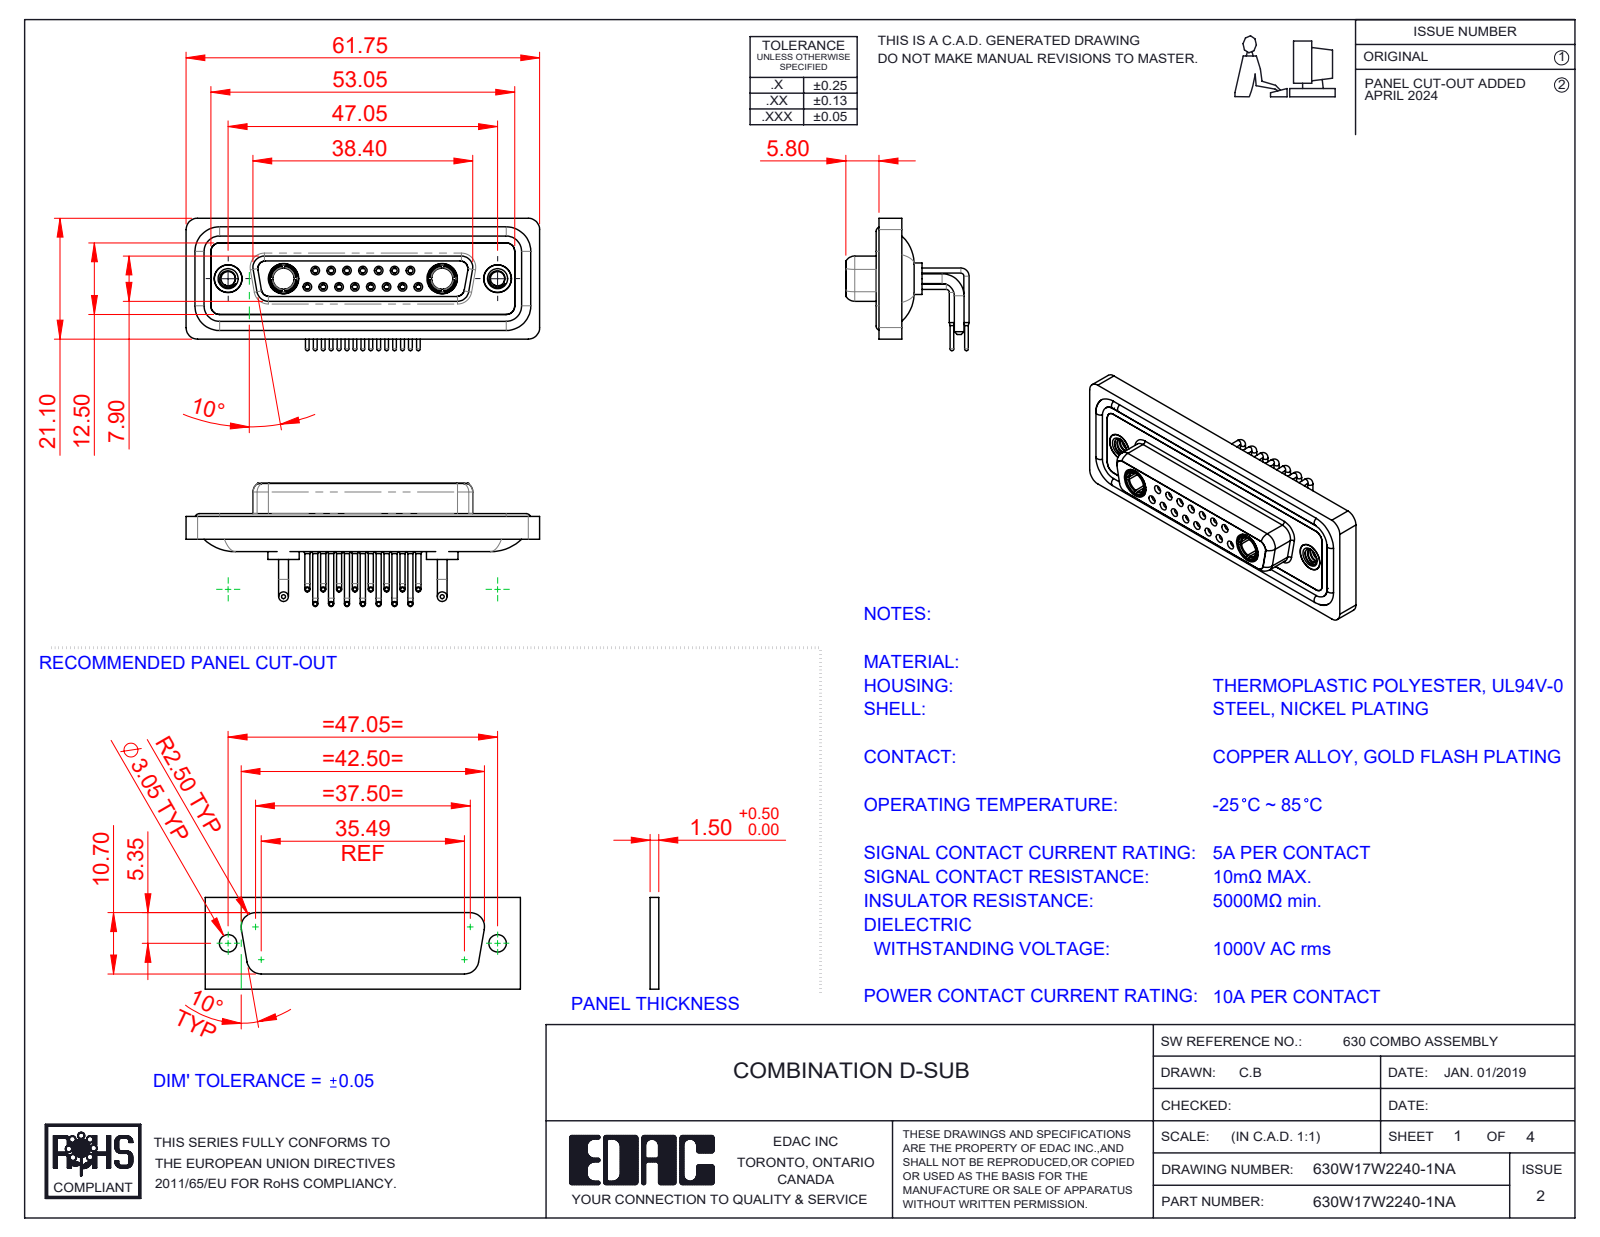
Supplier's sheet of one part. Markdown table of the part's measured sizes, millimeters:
| quantity | value |
| --- | --- |
| part name | 630Combo Shell Front_25 Contacts; 630Combo Waterproof Housing_25 Contacts; 630Combo Threaded Rivet_A; 630Combo Housing_17W2 (+5 more) |
| STEP written by | SolidWorks 2023 (CONFIG_CONTROL_DESIGN) |
| units | millimeters |
| bodies | 26 solids, 1331 faces (388 planar, 581 cylindrical, 362 other) |
| overall size | 61.75 × 23.12 × 21.53 |
| volume | 8 364 mm³ |
| surface area | 14 432 mm² |
| round holes (diameter × count) | 0.9 × 15, 1.1 × 15, 1.5 × 15, 2 × 15, 1.6 × 8, 1.7 × 7, 4.85 × 4, 2.5 × 2, 3.7 × 2, 4 × 2, 4.05 × 2, 5 × 2 |
| round bosses / shafts (diameter × count) | 0.9 × 15, 0.65 × 15, 1.6 × 11, 1.7 × 4, 5.5 × 2, 5.2 × 2, 4.96 × 2, 4.95 × 2 |
| partial cylindrical surfaces (radius × count) | 1.5 × 18, 2 × 18, 1.35 × 8, 1.6 × 8, 0.25 × 4, 0.5 × 4, 0.6 × 4, 0.65 × 4 |
| main face-to-face distances | 0.4, 1.8, 4.1, 1.1, 1.6, 1.5, 3.1, 2.5, 3.7, 1.4 |
| hole center spacings | 3.16, 2.77, 5.54, 8.31, 5.04, 7.49, 11.08, 5.03 |
